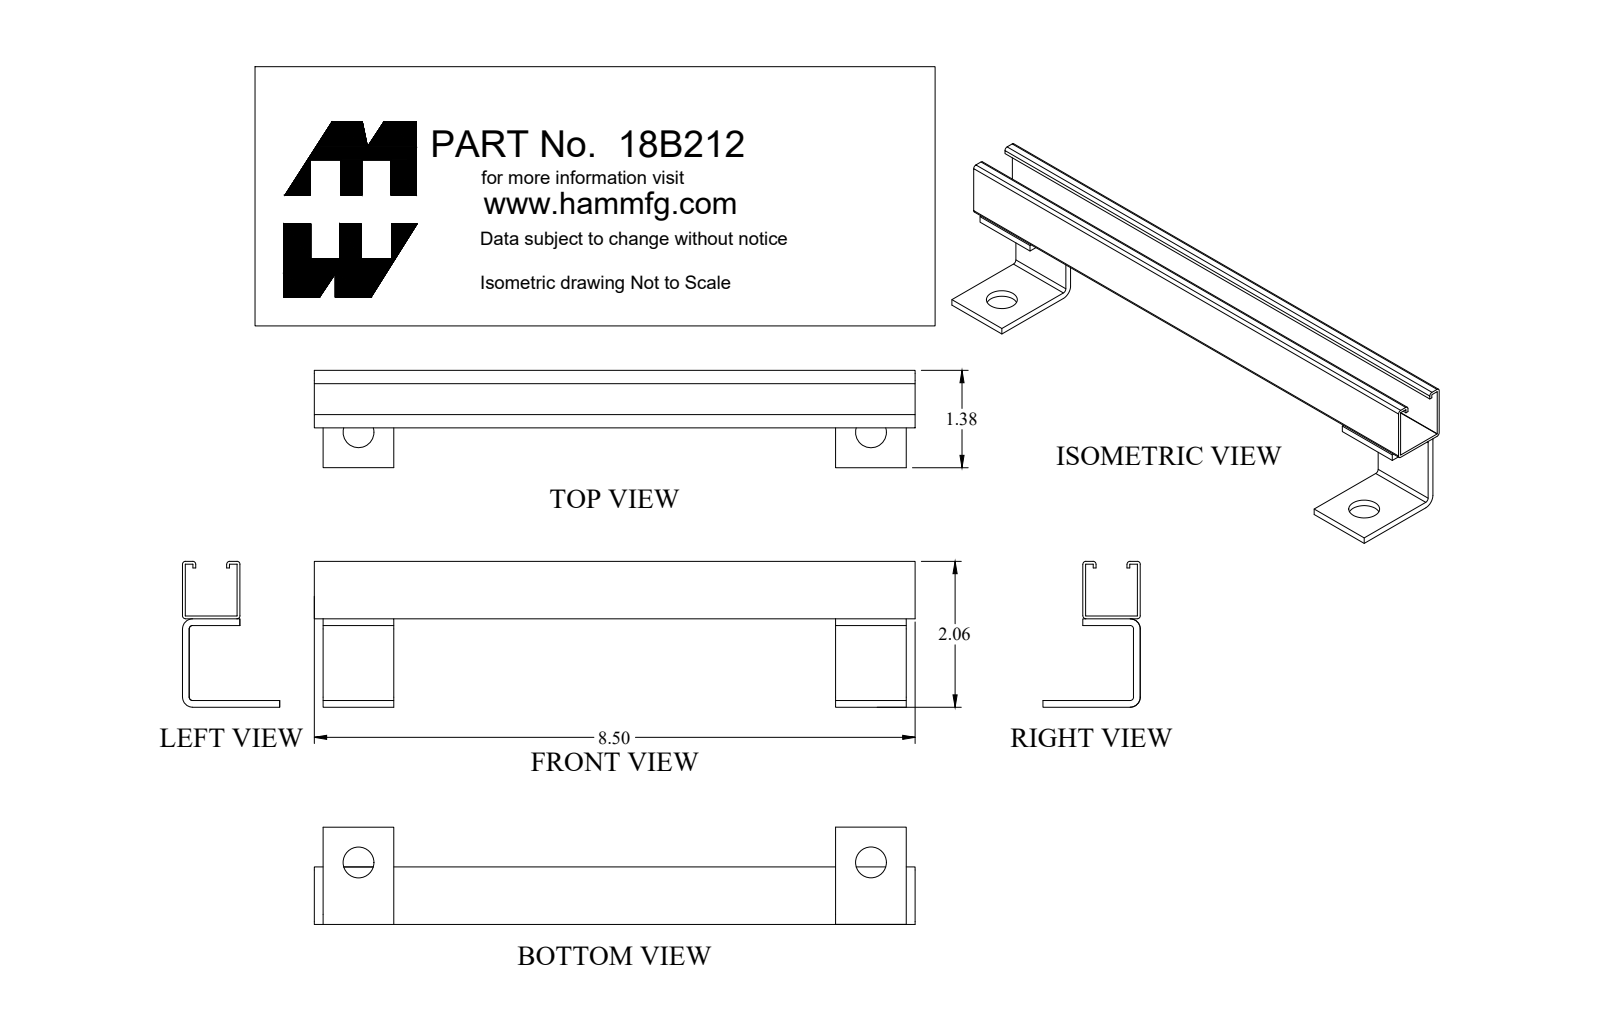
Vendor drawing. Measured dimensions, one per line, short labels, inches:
name: 18B212
written by: SolidWorks 2018 (AUTOMOTIVE_DESIGN)
unit: in
bodies: 3 solids, 60 faces (38 planar, 22 cylindrical, 0 other)
size: 8.5 × 2.063 × 1.376
volume: 1.492 in³; area: 60.76 in²
holes: 2× ⌀0.437
rounds: 6× R0.043, 4× R0.048, 4× R0.143
face distances: 0.04, 0.773, 0.813, 0.733, 0.095, 1.155, 0.773, 1.25, 1.29, 1.195
hole spacings: 7.25
